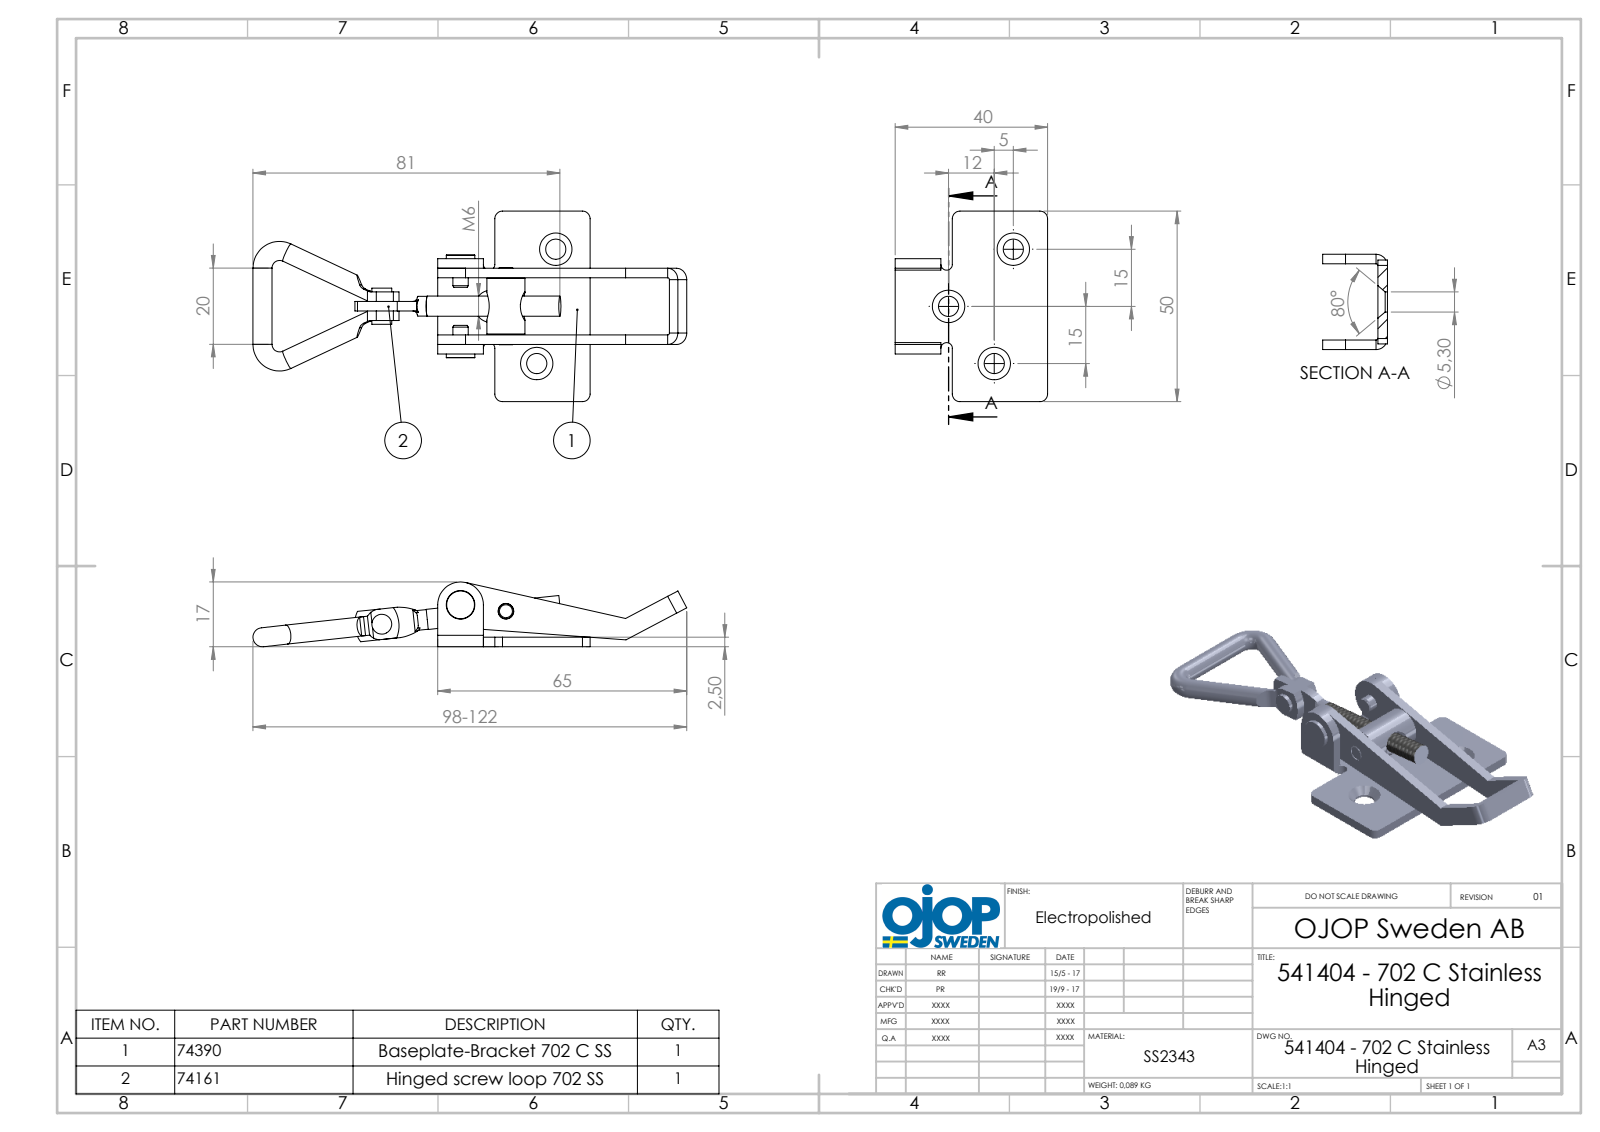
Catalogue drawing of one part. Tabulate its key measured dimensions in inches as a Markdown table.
| quantity | value |
| --- | --- |
| part name | 702 - C; 702 - Bygel; 702 - Ansatsnit; 702 - Rulle (+5 more) |
| STEP written by | SolidWorks 2015 (AUTOMOTIVE_DESIGN) |
| units | inches |
| bodies | 8 solids, 213 faces (82 planar, 103 cylindrical, 28 other) |
| overall size | 4.579 × 1.969 × 0.669 |
| volume | 0.703 in³ |
| surface area | 17.8 in² |
| round holes (diameter × count) | 0.161 × 3, 0.209 × 3, 0.197 × 1, 0.236 × 1 |
| round bosses / shafts (diameter × count) | 0.197 × 3, 0.157 × 2, 0.394 × 1, 0.295 × 1, 0.209 × 1, 0.205 × 1, 0.204 × 1 |
| partial cylindrical surfaces (radius × count) | 0.079 × 8, 0.039 × 6, 0.02 × 4, 0.118 × 4, 0.059 × 2, 0.267 × 2, 0.485 × 2, 0.152 × 1 |
| main face-to-face distances | 0.098, 0.689, 0.787, 0.591, 0.197, 0.343, 0.346, 0.441, 0.445, 0.886 |
| hole center spacings | 0.474, 0.756, 0.893, 0.924, 1.197, 1.381 |
